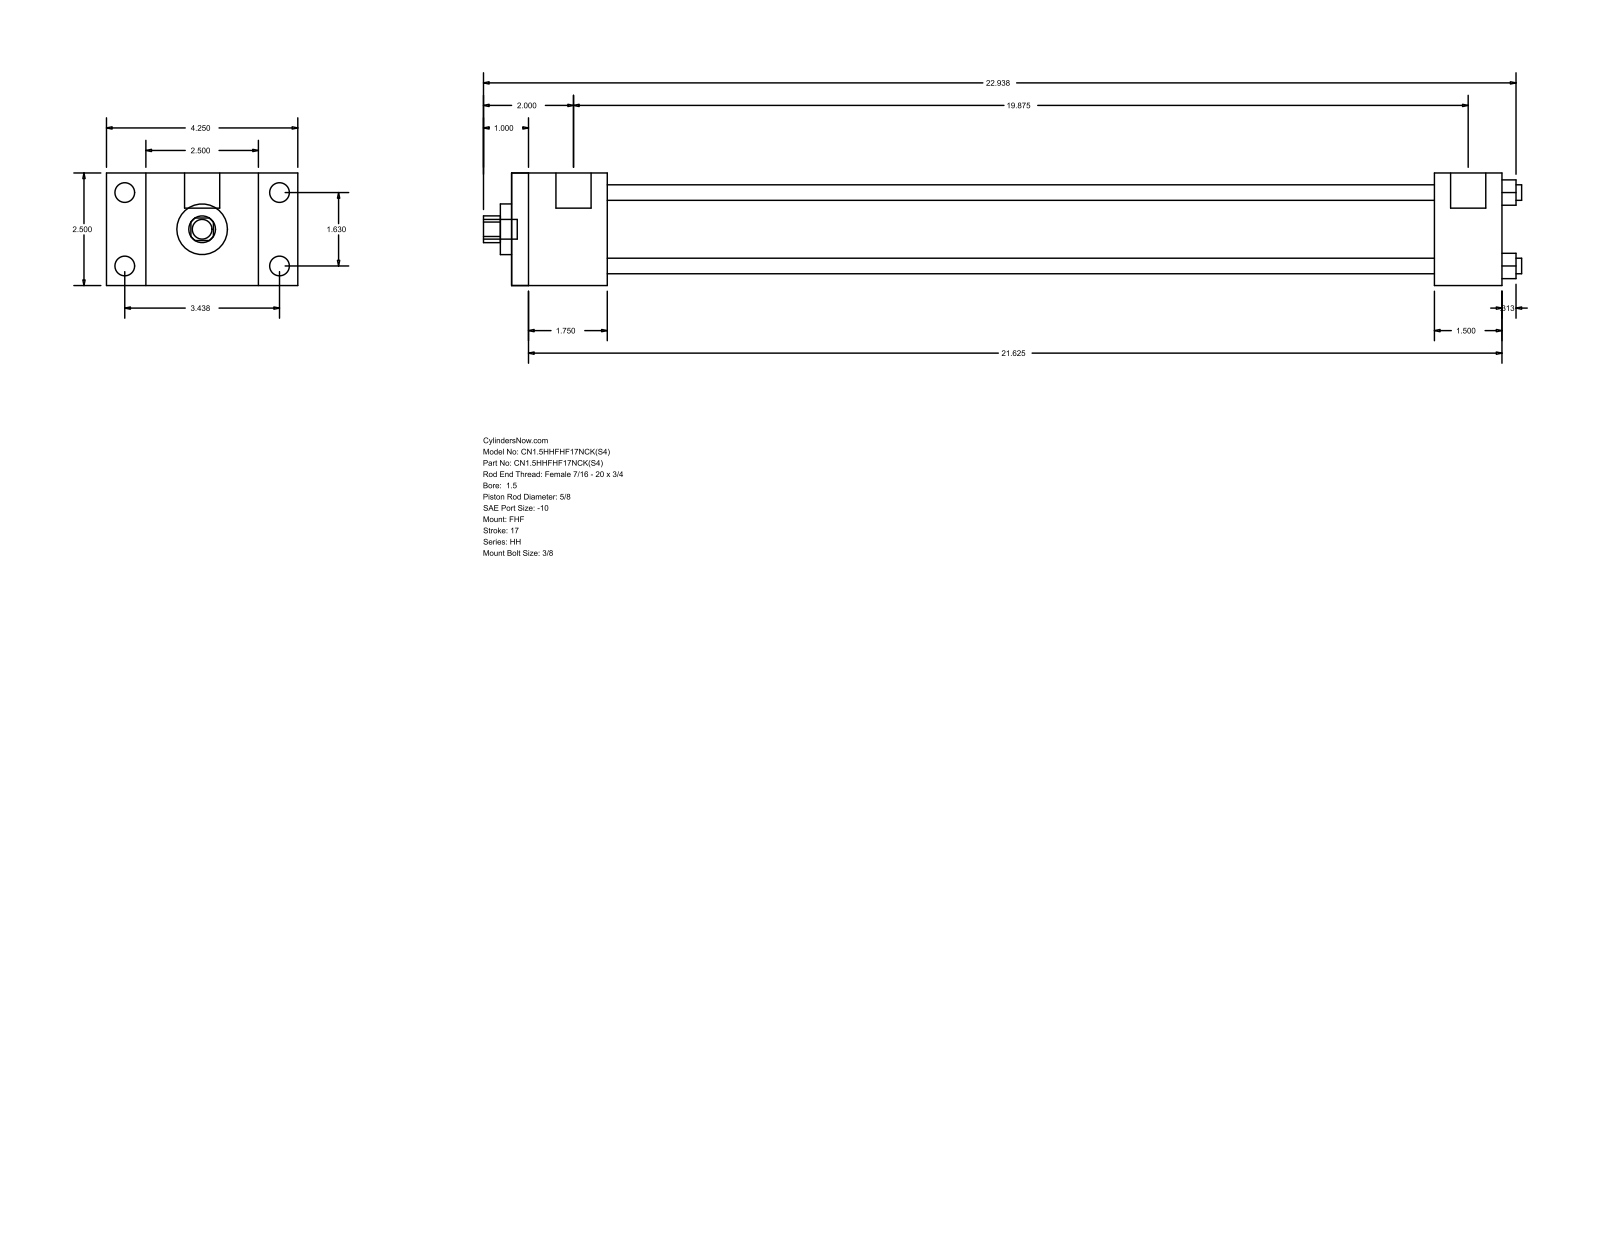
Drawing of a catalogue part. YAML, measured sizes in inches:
part_name: "HH_FHF__0150_0.625"
step_written_by: "GSSL Pune (CONFIG_CONTROL_DESIGN)"
units: inches
bodies: {solids: 0, faces: 88, planar: 60, cylindrical: 28, other: 0}
overall_size: [23.063, 4.25, 2.5]
round_holes:
  - {diameter: 0.345, count: 4}
  - {diameter: 0.625, count: 1}
  - {diameter: 1.125, count: 1}
  - {diameter: 1.75, count: 1}
round_bosses_or_shafts:
  - {diameter: 0.438, count: 4}
  - {diameter: 0.219, count: 4}
  - {diameter: 0.781, count: 2}
  - {diameter: 0.437, count: 1}
partial_cylinders:
  - {radius: 0.297, count: 1}
face_to_face_distances: [2.5, 0.875, 3.375, 2.125, 4.25, 22, 19.875, 20.5, 18.375, 1.5]
hole_center_spacings: [1.152, 1.63, 2.305]
